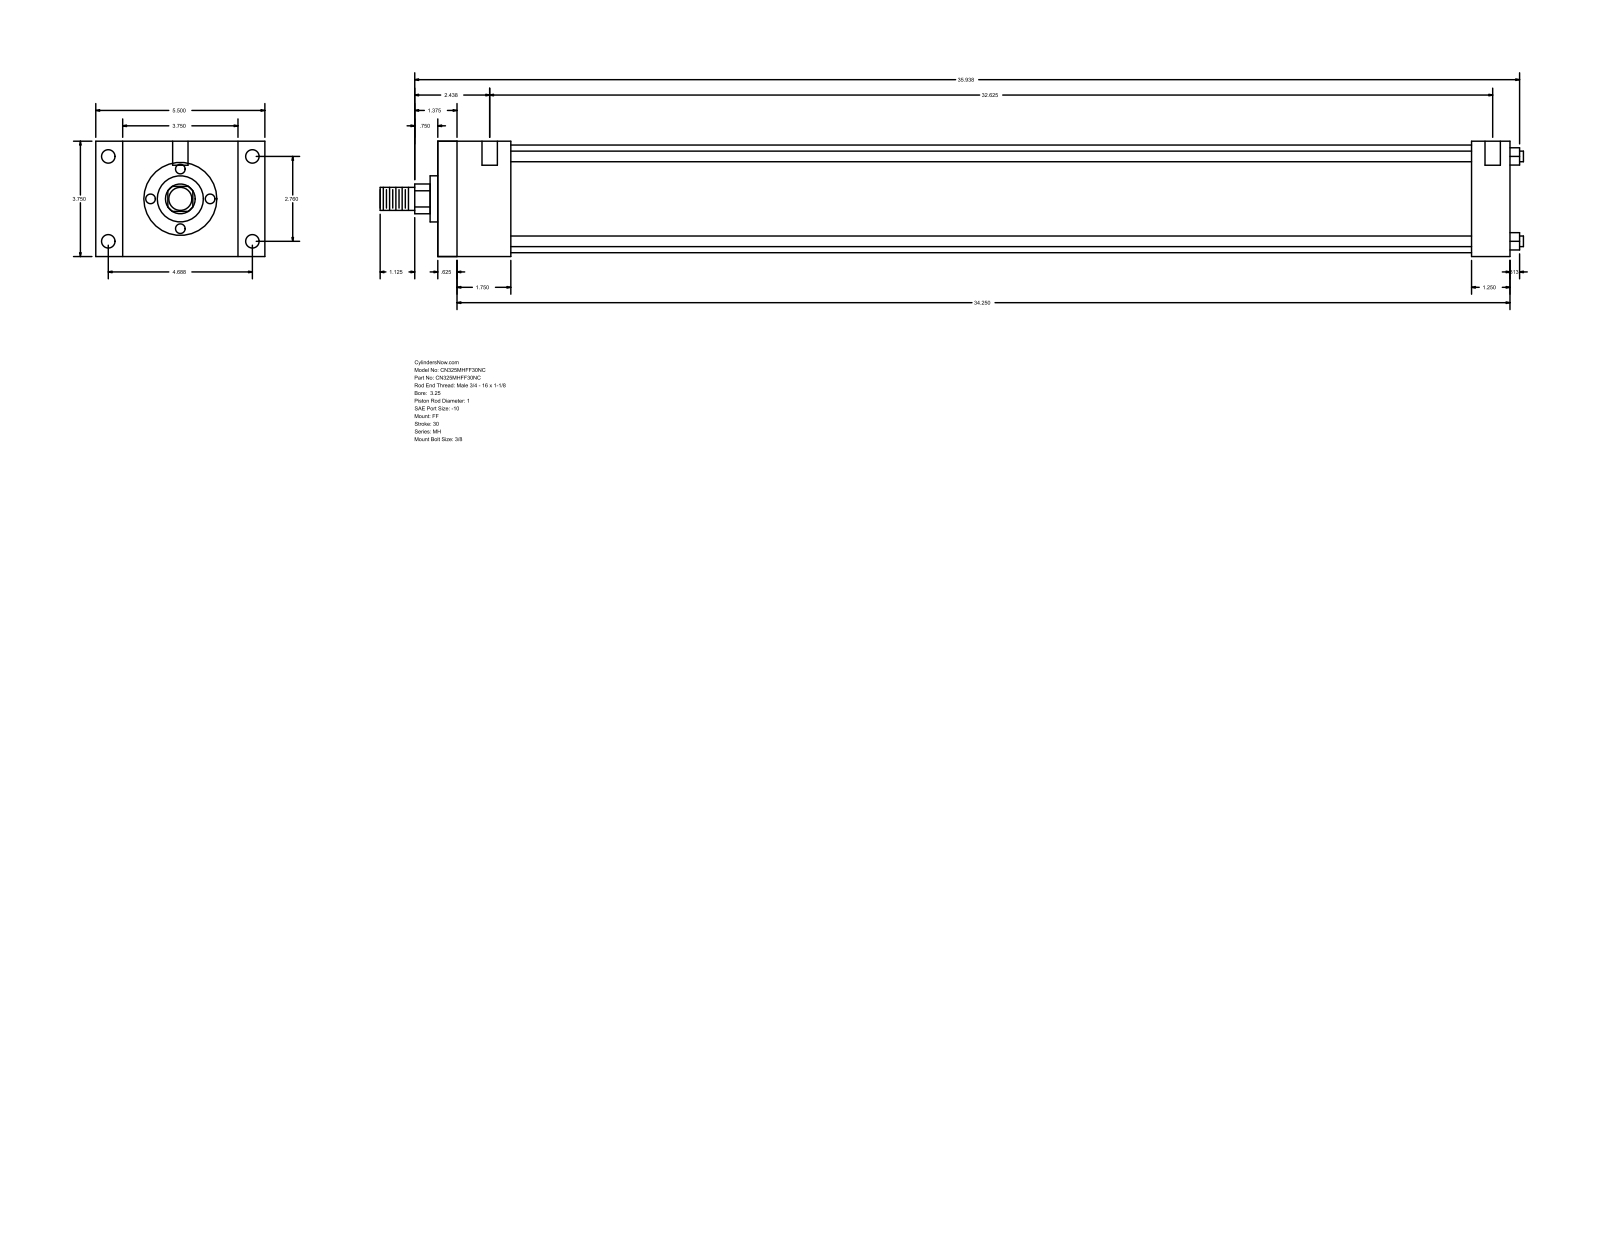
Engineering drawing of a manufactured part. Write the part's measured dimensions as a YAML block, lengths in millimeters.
part_name: "MH_FF__0325_1"
step_written_by: "GSSL Pune (CONFIG_CONTROL_DESIGN)"
units: millimeters
bodies: {solids: 0, faces: 92, planar: 64, cylindrical: 28, other: 0}
overall_size: [944.56, 139.7, 95.25]
round_holes:
  - {diameter: 5.56, count: 4}
  - {diameter: 11.13, count: 4}
  - {diameter: 12.7, count: 2}
round_bosses_or_shafts:
  - {diameter: 8.76, count: 4}
  - {diameter: 88.9, count: 1}
  - {diameter: 38.1, count: 1}
  - {diameter: 25.4, count: 1}
  - {diameter: 19.05, count: 1}
partial_cylinders:
  - {radius: 12.29, count: 1}
face_to_face_distances: [95.24, 885.83, 15.87, 869.96, 22.23, 117.47, 854.07, 838.2, 31.76, 60.33]
hole_center_spacings: [70.1, 119.06, 138.16, 835.02, 1.58, 4.76, 828.68, 830.26]
